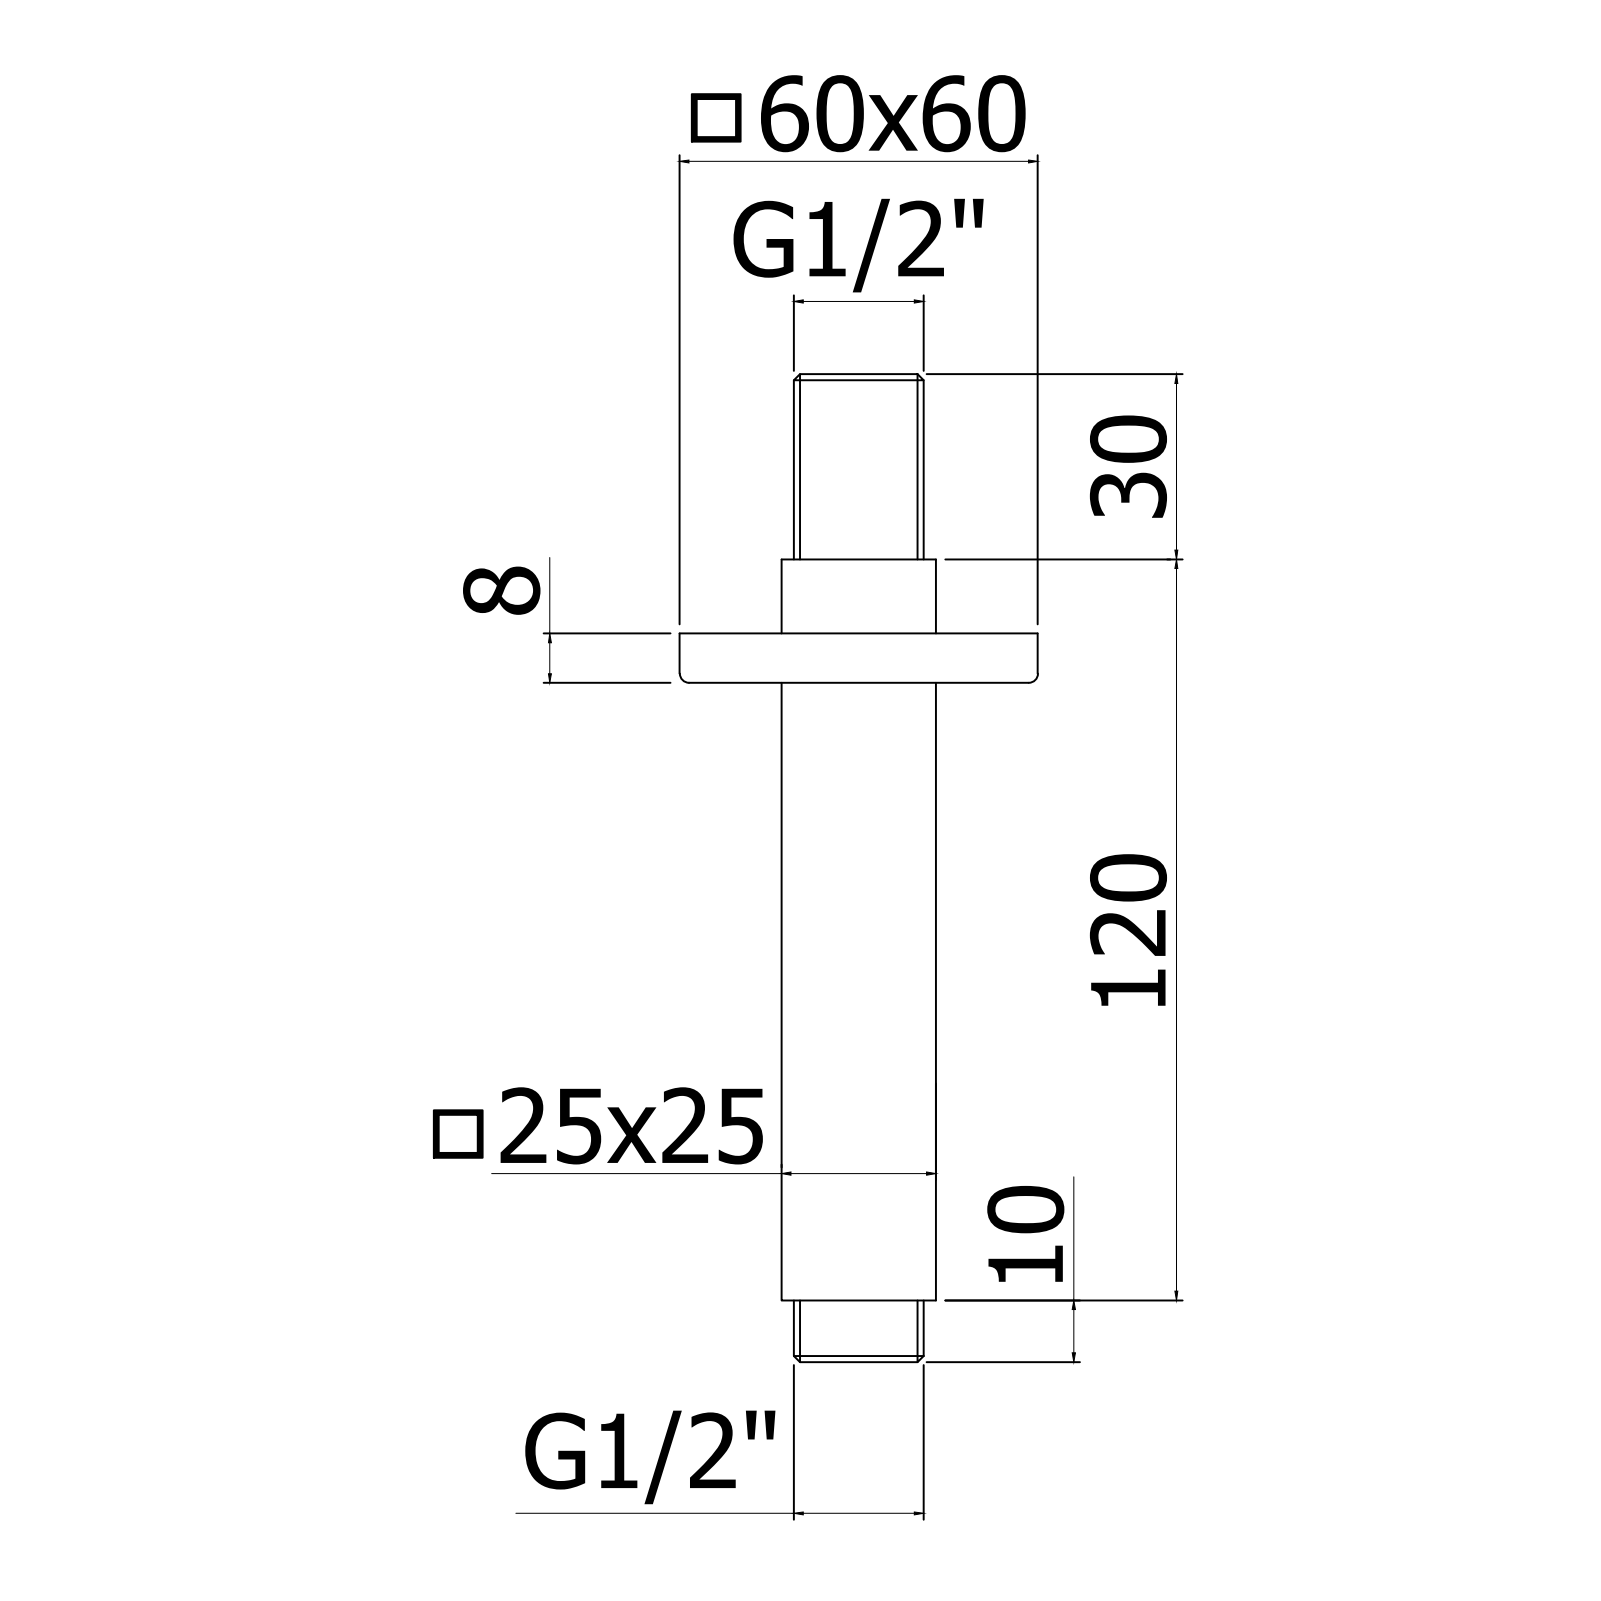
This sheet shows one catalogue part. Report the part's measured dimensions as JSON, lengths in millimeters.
{"part_name": "ZSOF118CR", "step_written_by": "CREO PARAMETRIC BY PTC INC, 2020044 (CONFIG_CONTROL_DESIGN)", "units": "millimeters", "bodies": {"solids": 1, "faces": 21, "planar": 13, "cylindrical": 4, "other": 4}, "overall_size": [130, 60, 60], "volume_mm3": 101961, "surface_area_mm2": 21113, "round_bosses_or_shafts": [[21, 1], [17, 1]], "face_to_face_distances": [25, 8, 17.5, 42.5, 60, 112, 120, 122, 10, 130]}
